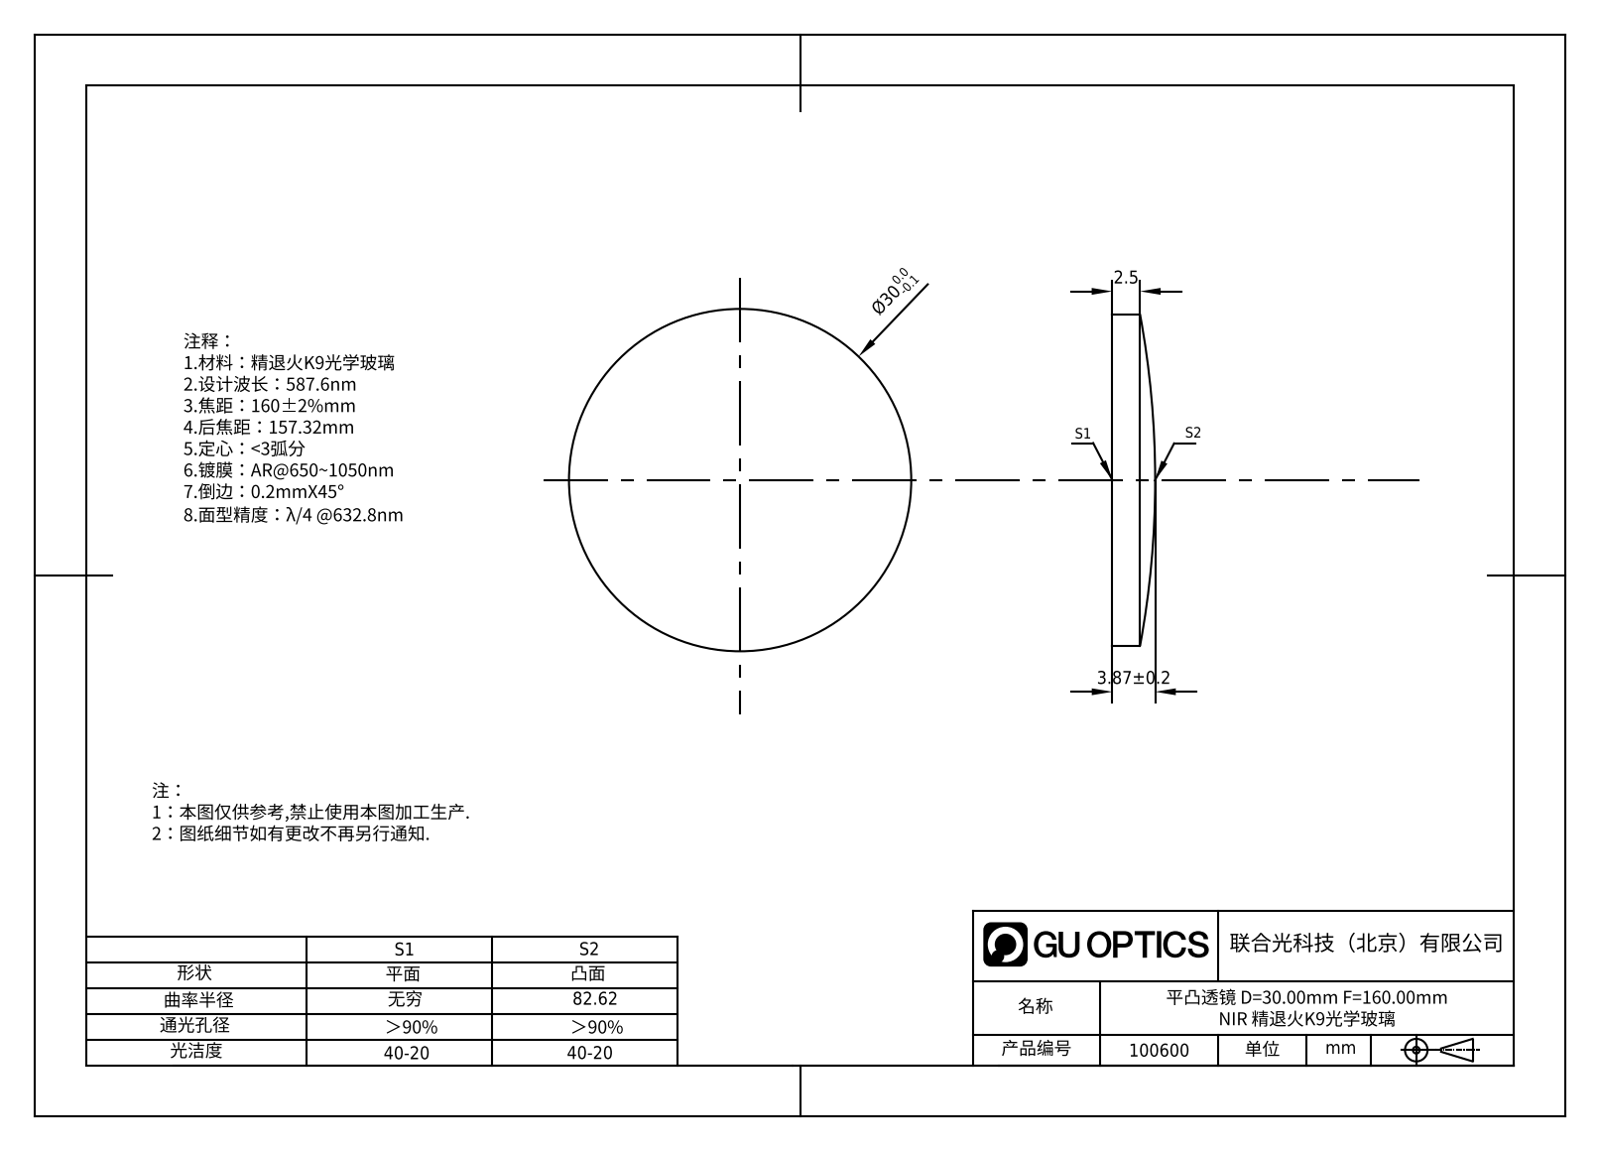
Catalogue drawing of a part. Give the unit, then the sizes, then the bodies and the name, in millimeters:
Units: millimetres
Overall size (bounding box): 30 × 30 × 3.87
Round bosses / shafts (diameter × count): ⌀30 ×1
Volume: 2 253 mm³ · Surface area: 1 655 mm²
Bodies: 1 solid, 5 faces (1 planar, 2 cylindrical, 2 other)
Part name (STEP PRODUCT): 100600
STEP written by: SolidWorks 2020 (CONFIG_CONTROL_DESIGN)
